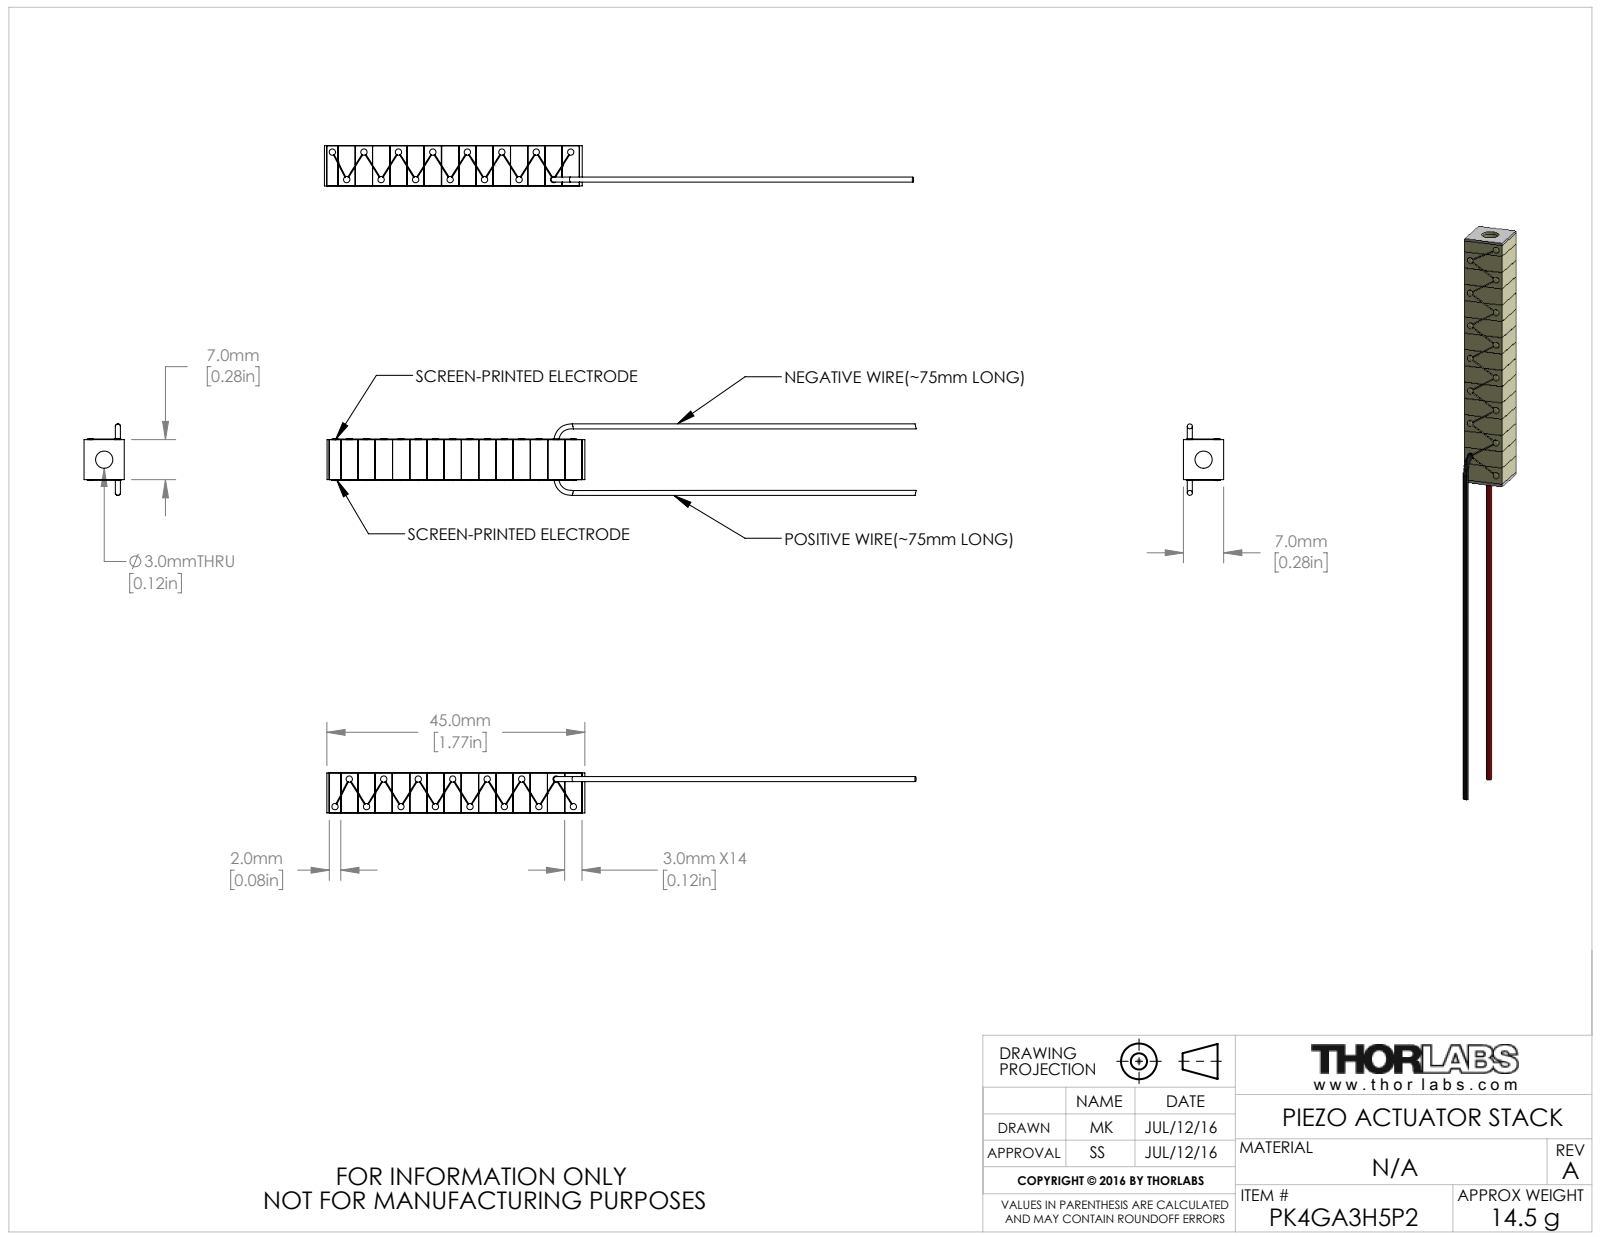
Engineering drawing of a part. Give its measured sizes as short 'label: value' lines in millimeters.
name: CTN009269
written by: SolidWorks 2016 (AUTOMOTIVE_DESIGN)
unit: mm
bodies: 4 solids, 564 faces (282 planar, 158 cylindrical, 124 other)
size: 102.88 × 12.48 × 7
volume: 3 805 mm³; area: 6 428 mm²
holes: 1× ⌀3, 1× ⌀3.1
bosses: 15× ⌀1.1
face distances: 7, 3.01, 6.02, 9.03, 12.04, 3, 6.01, 9.02, 15.05, 15.04
